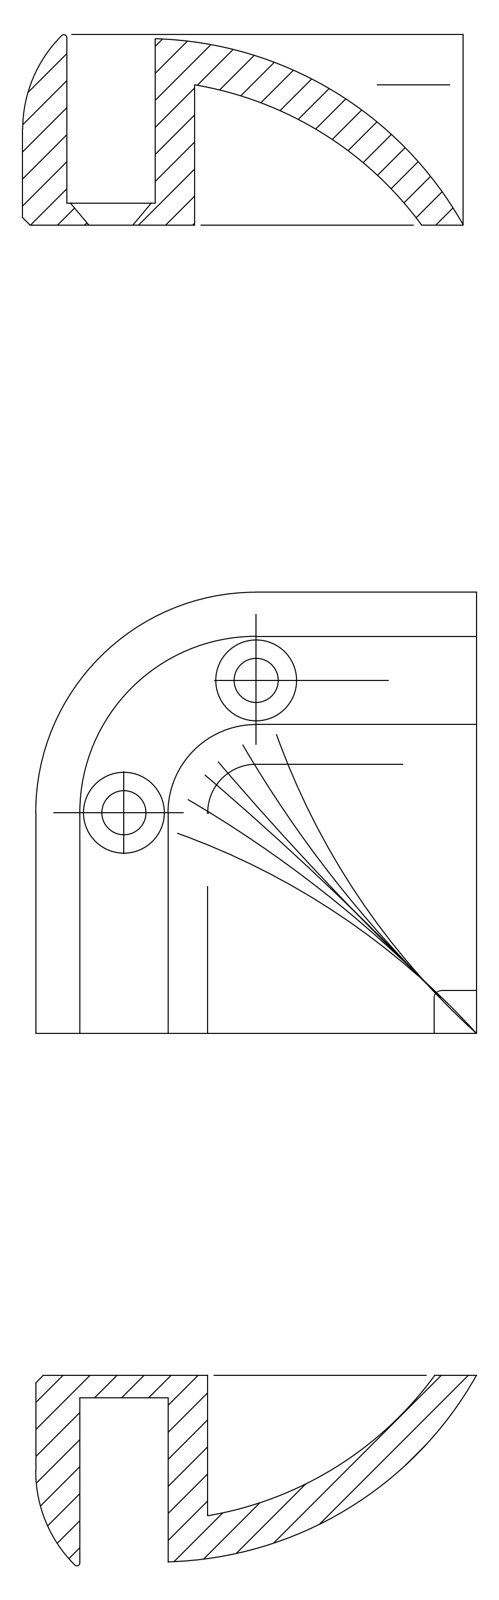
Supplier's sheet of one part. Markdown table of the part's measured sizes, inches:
| quantity | value |
| --- | --- |
| STEP written by | THINKDESIGN (CONFIG_CONTROL_DESIGN) |
| units | inches |
| bodies | 1 solid, 39 faces (18 planar, 12 cylindrical, 9 other) |
| overall size | 1.18 × 1.18 × 0.51 |
| volume | 0.397 in³ |
| surface area | 5.915 in² |
| partial cylindrical surfaces (radius × count) | 0.008 × 4, 0.354 × 2, 0.978 × 2, 0.13 × 1, 0.236 × 1, 0.472 × 1, 0.591 × 1 |
| main face-to-face distances | 1.062, 0.236, 0.826, 0.039, 0.059, 0.02, 0.118, 0.354, 1.18, 0.606 |
